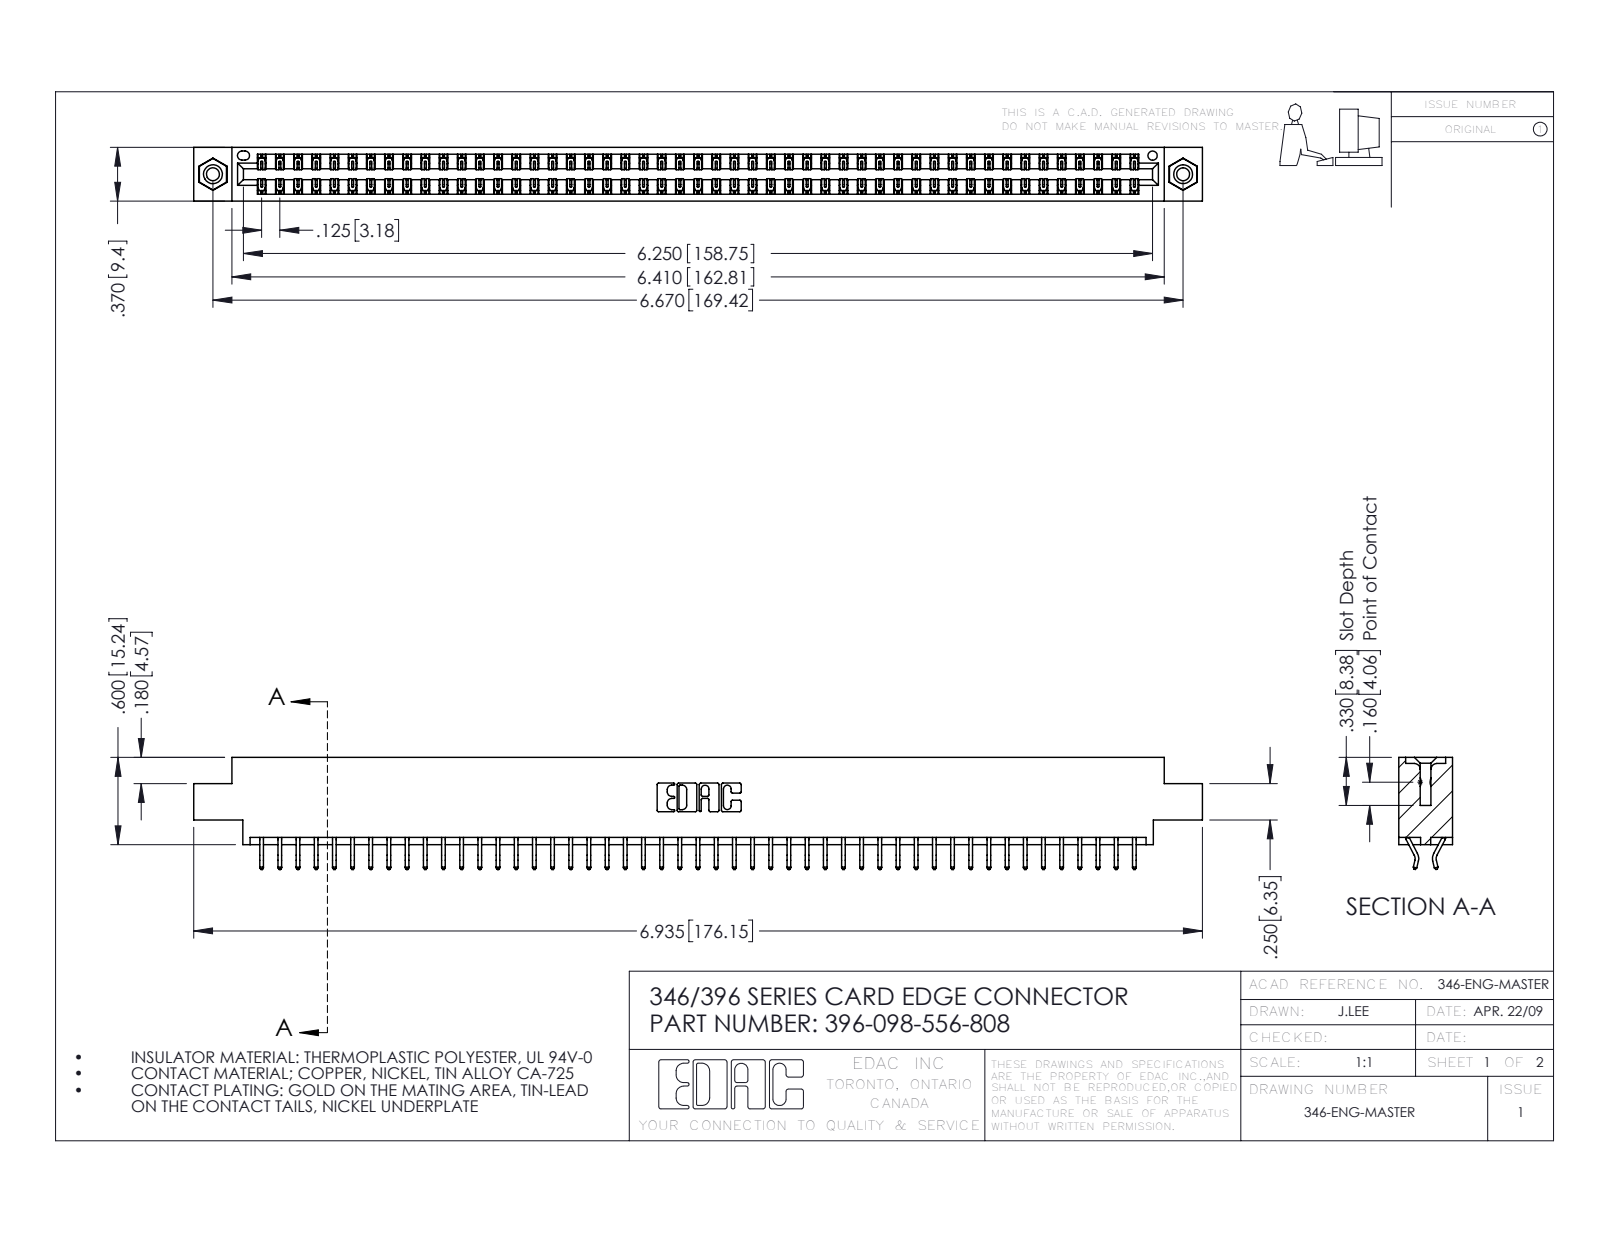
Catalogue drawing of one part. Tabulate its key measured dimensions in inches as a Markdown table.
| quantity | value |
| --- | --- |
| part name | 346 Part_0.170 Offset - 0.156 Dia-TI; 345-292-001_556 Tail; 345-250-001_345-250-003-102; 396-098-556-808 |
| STEP written by | SolidWorks 2016 (CONFIG_CONTROL_DESIGN) |
| units | inches |
| bodies | 101 solids, 5870 faces (3934 planar, 1920 cylindrical, 16 other) |
| overall size | 6.935 × 0.77 × 0.37 |
| volume | 1.041 in³ |
| surface area | 36.7 in² |
| round holes (diameter × count) | 0.089 × 2, 0.125 × 2, 0.156 × 2, 0.064 × 1 |
| round bosses / shafts (diameter × count) | 0.155 × 2 |
| partial cylindrical surfaces (radius × count) | 0.006 × 147, 0.01 × 22, 0.007 × 6, 0.031 × 6, 0.026 × 3, 0.01 × 2, 0.014 × 2, 0.022 × 2 |
| main face-to-face distances | 0.048, 0.322, 0.37, 0.25, 0.025, 0.072, 0.298, 0.275, 0.222, 0.148 |
| hole center spacings | 0.246, 6.461, 6.67 |
